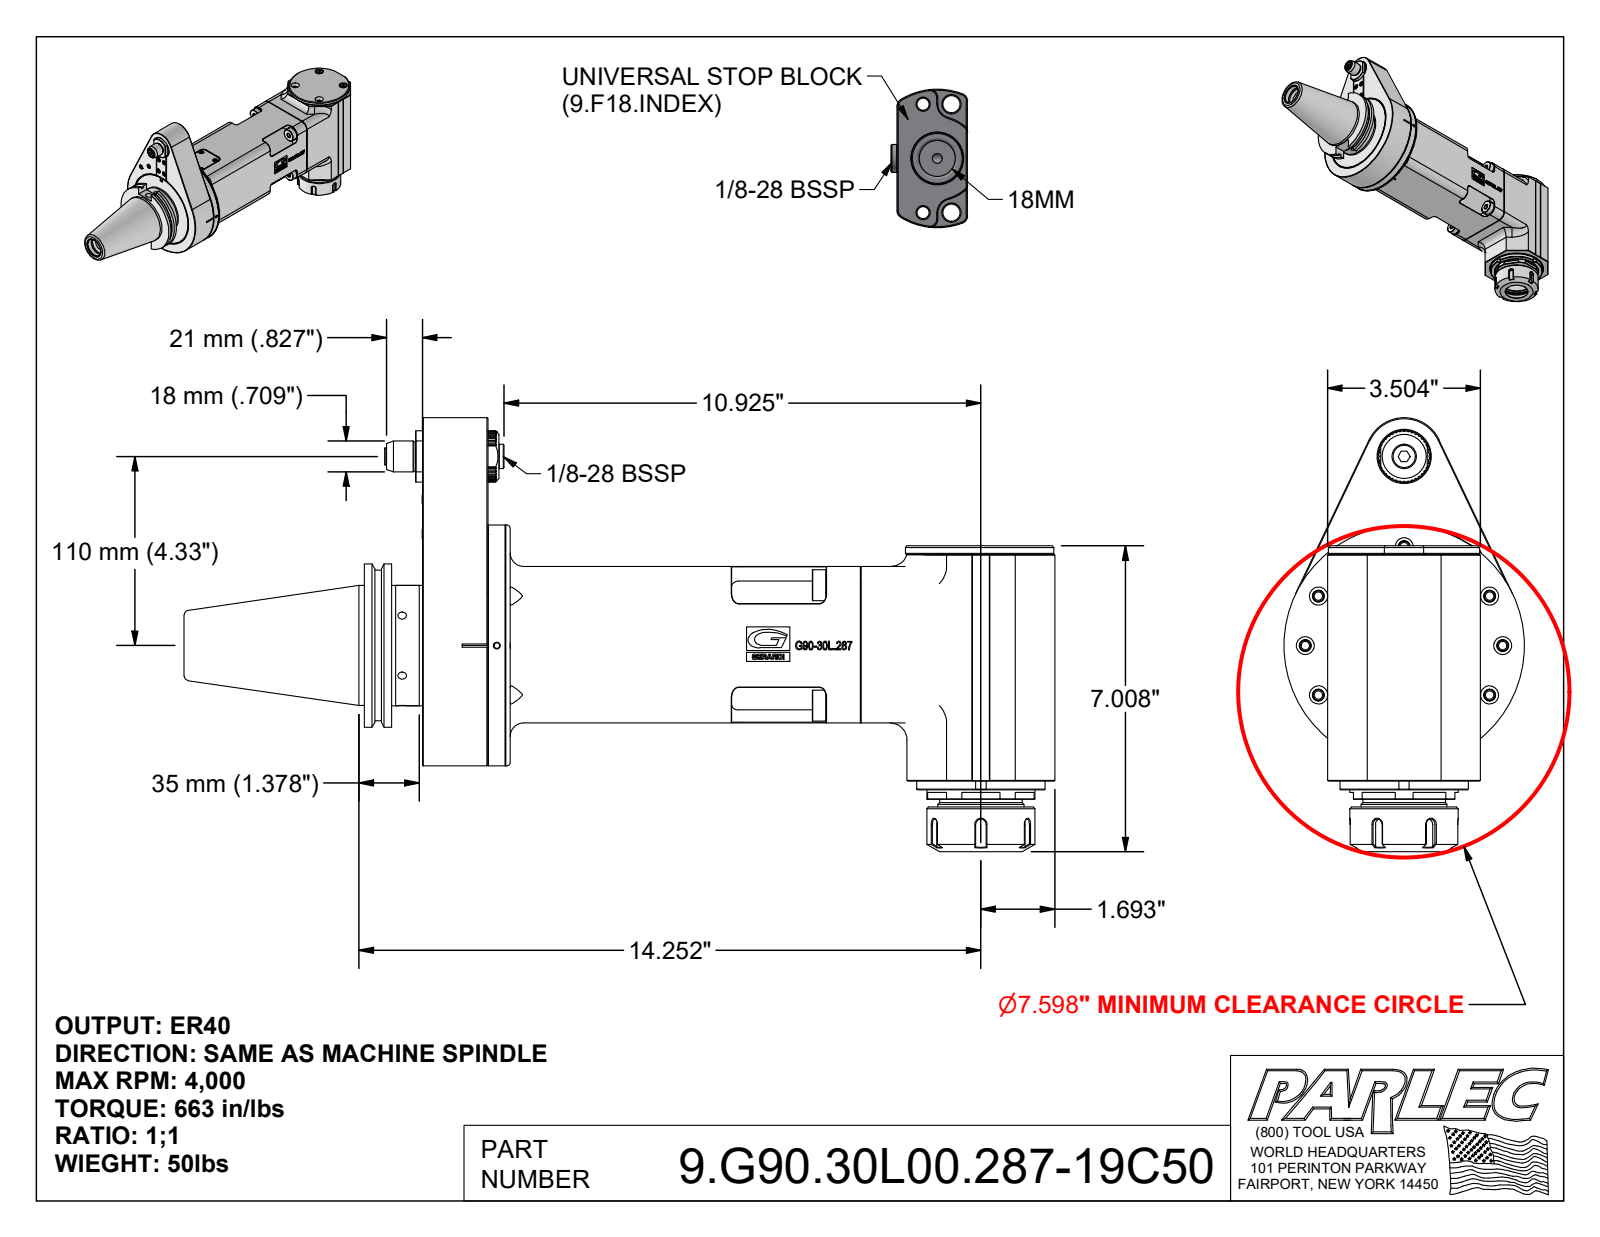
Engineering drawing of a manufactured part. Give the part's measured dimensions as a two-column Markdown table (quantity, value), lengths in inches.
| quantity | value |
| --- | --- |
| part name | 9.G90.30L00.287-19C50; 9_G90_30L0-287; 9_GA3_451_1 (Classic, Type 3, Cat50, 110mm) |
| STEP written by | Autodesk Inventor 2022 (AUTOMOTIVE_DESIGN) |
| units | inches |
| bodies | 45 solids, 2402 faces (968 planar, 547 cylindrical, 887 other) |
| overall size | 19.953 × 9.941 × 5.512 |
| volume | 162.9 in³ |
| surface area | 853.2 in² |
| round holes (diameter × count) | 0.256 × 16, 0.197 × 14, 0.165 × 11, 0.157 × 10, 0.236 × 9, 0.413 × 8, 0.13 × 7, 0.098 × 6, 0.118 × 6, 0.335 × 3, 0.059 × 2, 0.205 × 2 |
| round bosses / shafts (diameter × count) | 0.228 × 8, 0.709 × 4, 1.181 × 2, 0.551 × 2, 0.504 × 2, 0.394 × 2, 0.386 × 2, 0.354 × 2 |
| partial cylindrical surfaces (radius × count) | 0.039 × 56, 0.118 × 22, 0.394 × 10, 0.157 × 8, 0.236 × 8, 0.374 × 7, 0.392 × 7, 0.315 × 4 |
| main face-to-face distances | 3.504, 0.157, 3.583, 1.496, 0.315, 0.236, 1.102, 0.626, 0.591, 0.039 |
| hole center spacings | 2.264, 3.202, 3.921, 4.373, 1.172, 1.32, 0.934, 0.571 |
